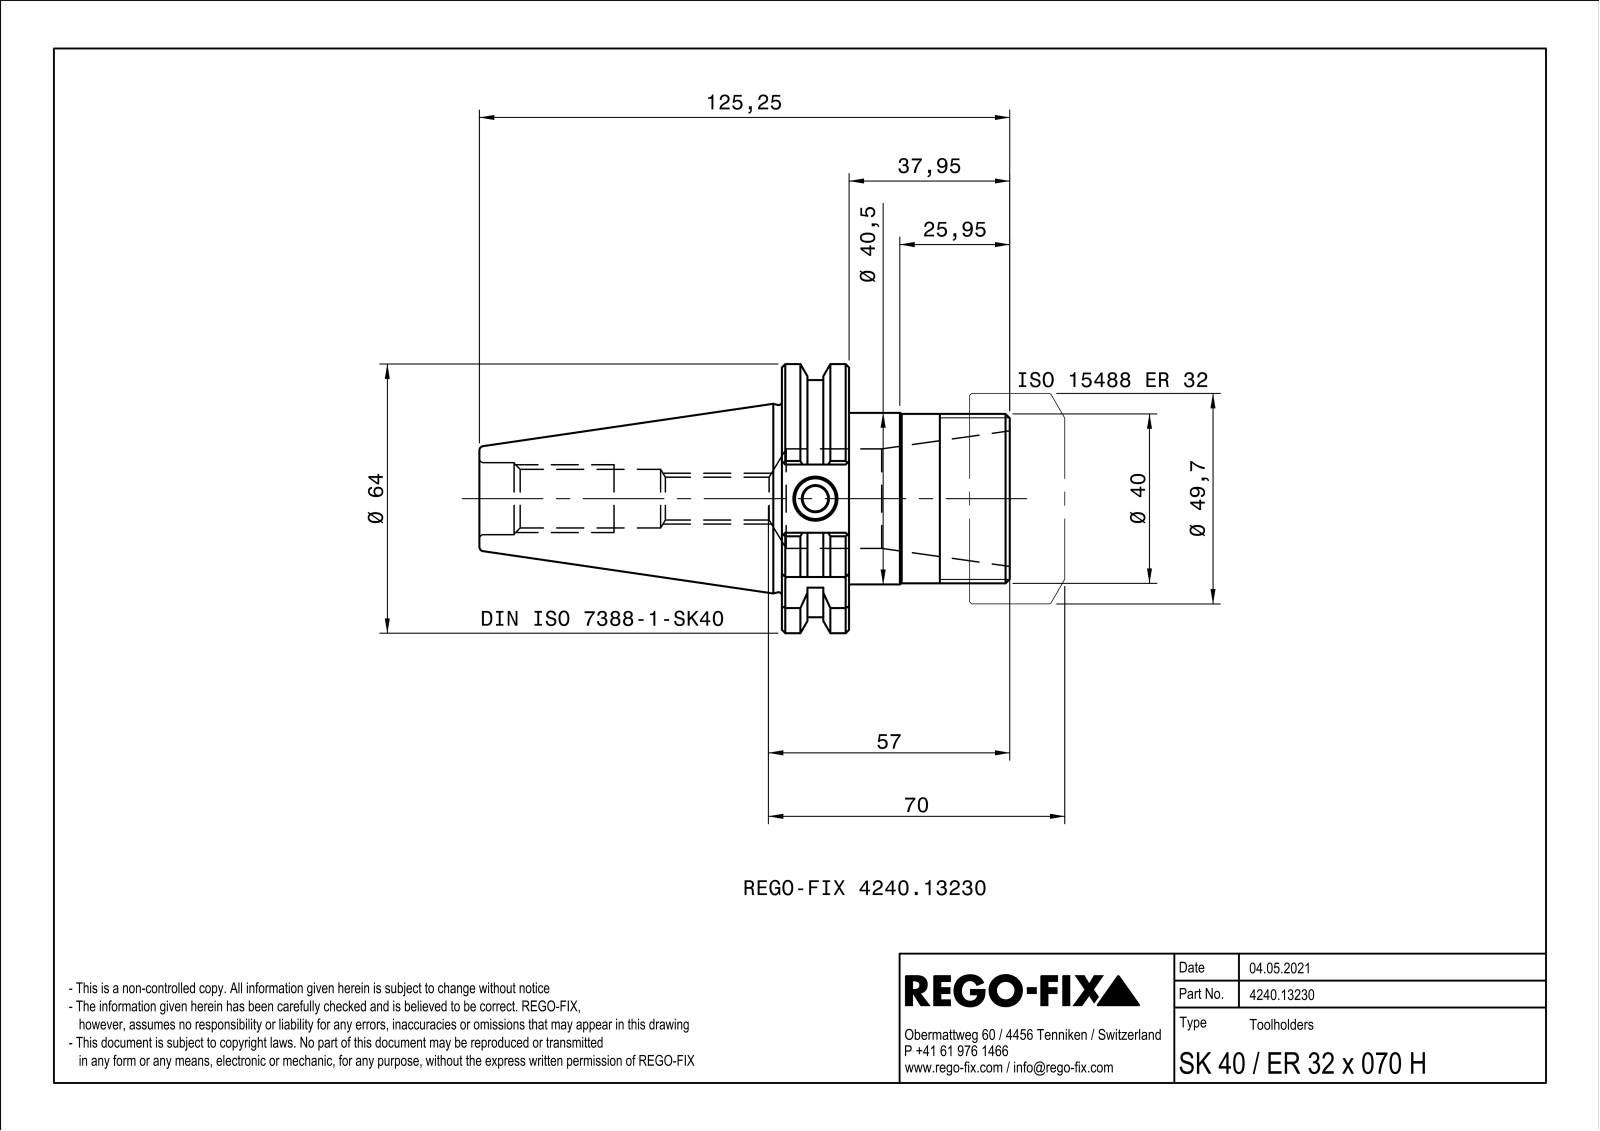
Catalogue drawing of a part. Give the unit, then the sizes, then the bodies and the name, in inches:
Units: inches
Overall size (bounding box): 4.931 × 2.502 × 2.402
Round holes (diameter × count): ⌀0.138 ×5, ⌀0.236 ×1, ⌀0.394 ×1, ⌀0.398 ×1, ⌀0.544 ×1, ⌀0.545 ×1, ⌀0.669 ×1, ⌀0.925 ×1
Round bosses / shafts (diameter × count): ⌀1.594 ×1, ⌀1.575 ×1
Partial cylindrical surfaces — rounded edges, fillets, slot ends (radius × count): R0.02 ×13, R1.102 ×1, R1.251 ×1
Main face-to-face distances: 0.624, 1.494, 2.118, 1.862, 0.634, 4.931, 3.437, 2.813, 0.411, 1.045
Volume: 7.447 in³ · Surface area: 43.99 in²
Bodies: 1 solid, 133 faces (40 planar, 44 cylindrical, 49 other)
Part name (STEP PRODUCT): NOCUT
STEP written by: SIEMENS PLM Software Solid Edge ST10 (AUTOMOTIVE_DESIGN)
